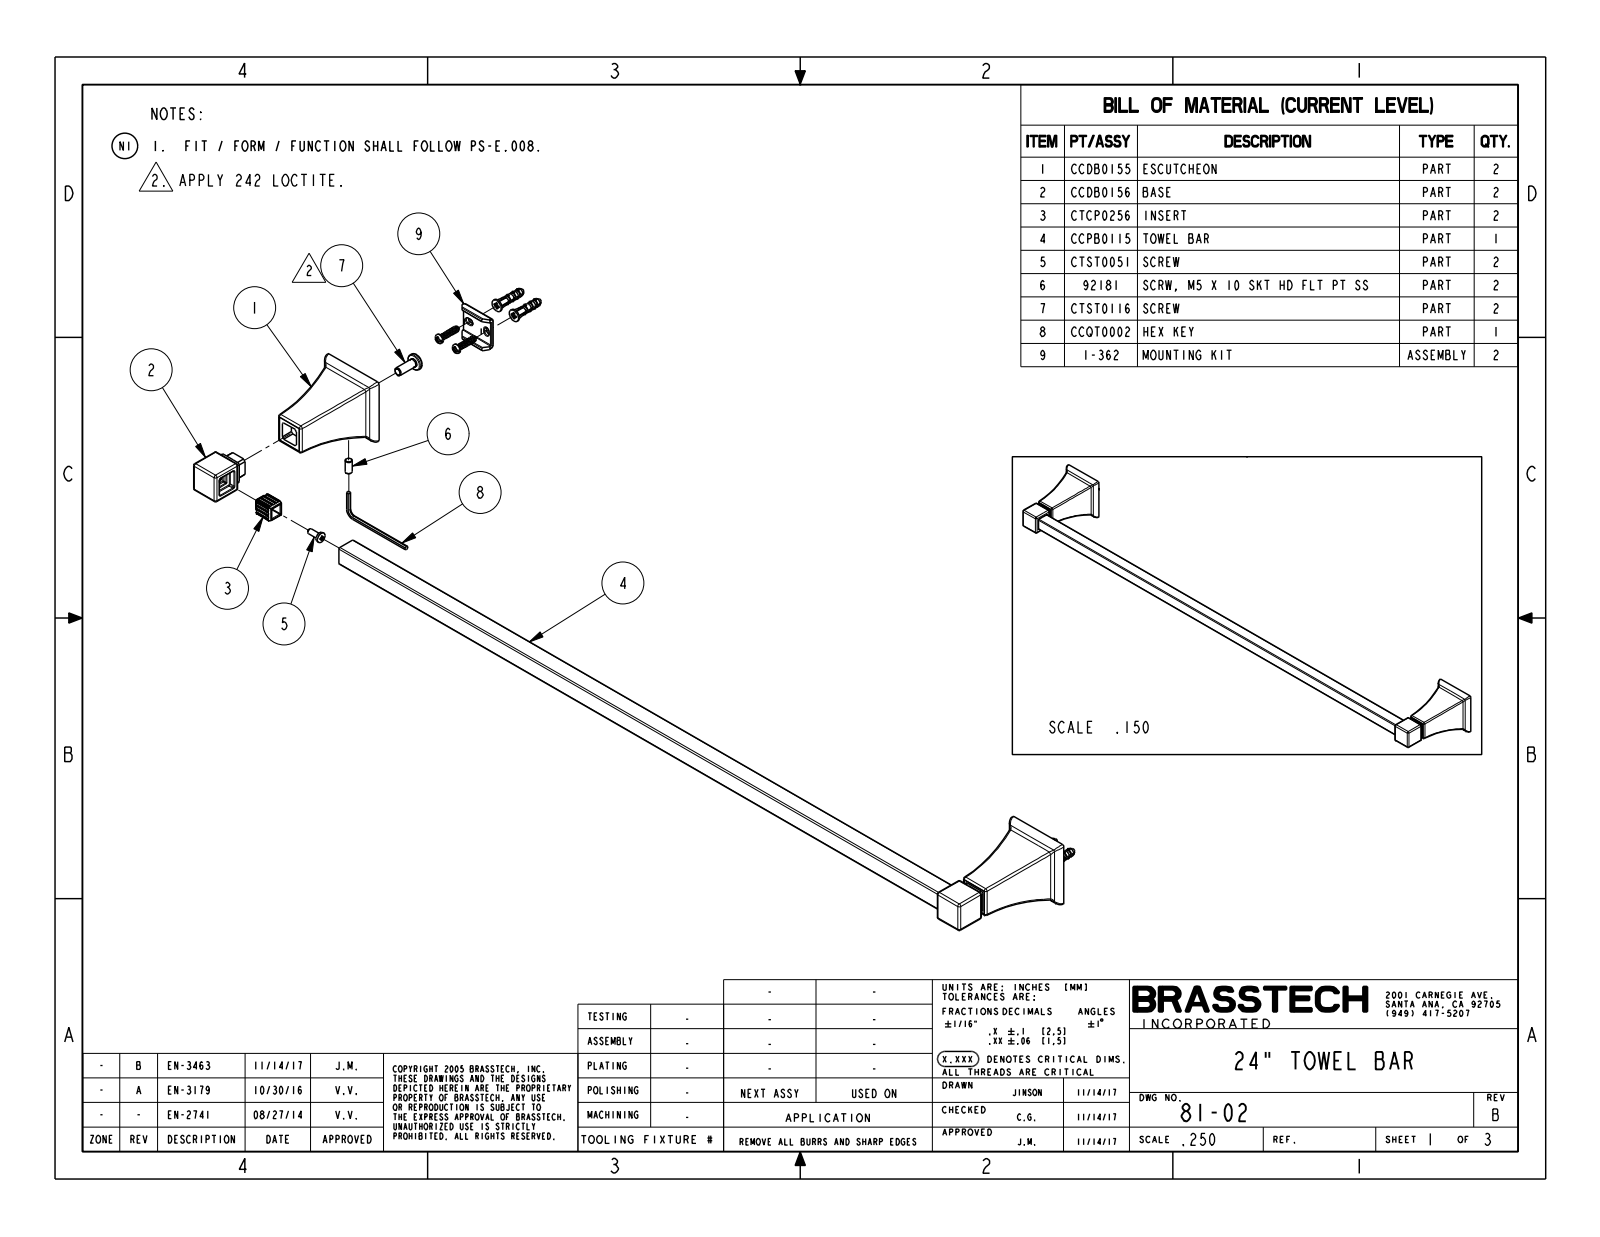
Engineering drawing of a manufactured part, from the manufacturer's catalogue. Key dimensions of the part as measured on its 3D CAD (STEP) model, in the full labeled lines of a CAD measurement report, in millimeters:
Part name (STEP PRODUCT): CCDB0155; CCDB0156; CTCP0256; CCPB0115 (+5 more)
STEP written by: PRO/ENGINEER BY PARAMETRIC TECHNOLOGY CORPORATION, 2013150 (CONFIG_CONTROL_DESIGN)
Units: millimetres
Bodies: 15 solids, 1492 faces (376 planar, 672 cylindrical, 444 other)
Overall size (bounding box): 662.3 × 89 × 50.8
Volume: 96 390 mm³ · Surface area: 116 600 mm²
Round holes (diameter × count): ⌀4.2 ×3, ⌀5 ×2, ⌀6 ×2, ⌀6.5 ×2, ⌀10 ×2, ⌀3.2 ×1
Round bosses / shafts (diameter × count): ⌀12 ×2, ⌀6 ×2, ⌀5 ×2, ⌀4 ×1
Partial cylindrical surfaces — rounded edges, fillets, slot ends (radius × count): R0.3 ×188, R0.5 ×152, R1.5 ×34, R2.3 ×8, R4 ×6, R5.3 ×6, R5.5 ×6, R6.8 ×6
Main face-to-face distances: 1, 13.3, 14.3, 12.3, 4.1, 5.1, 17.4, 18.4, 2.5, 20.9
Hole centre spacings: 611.5
